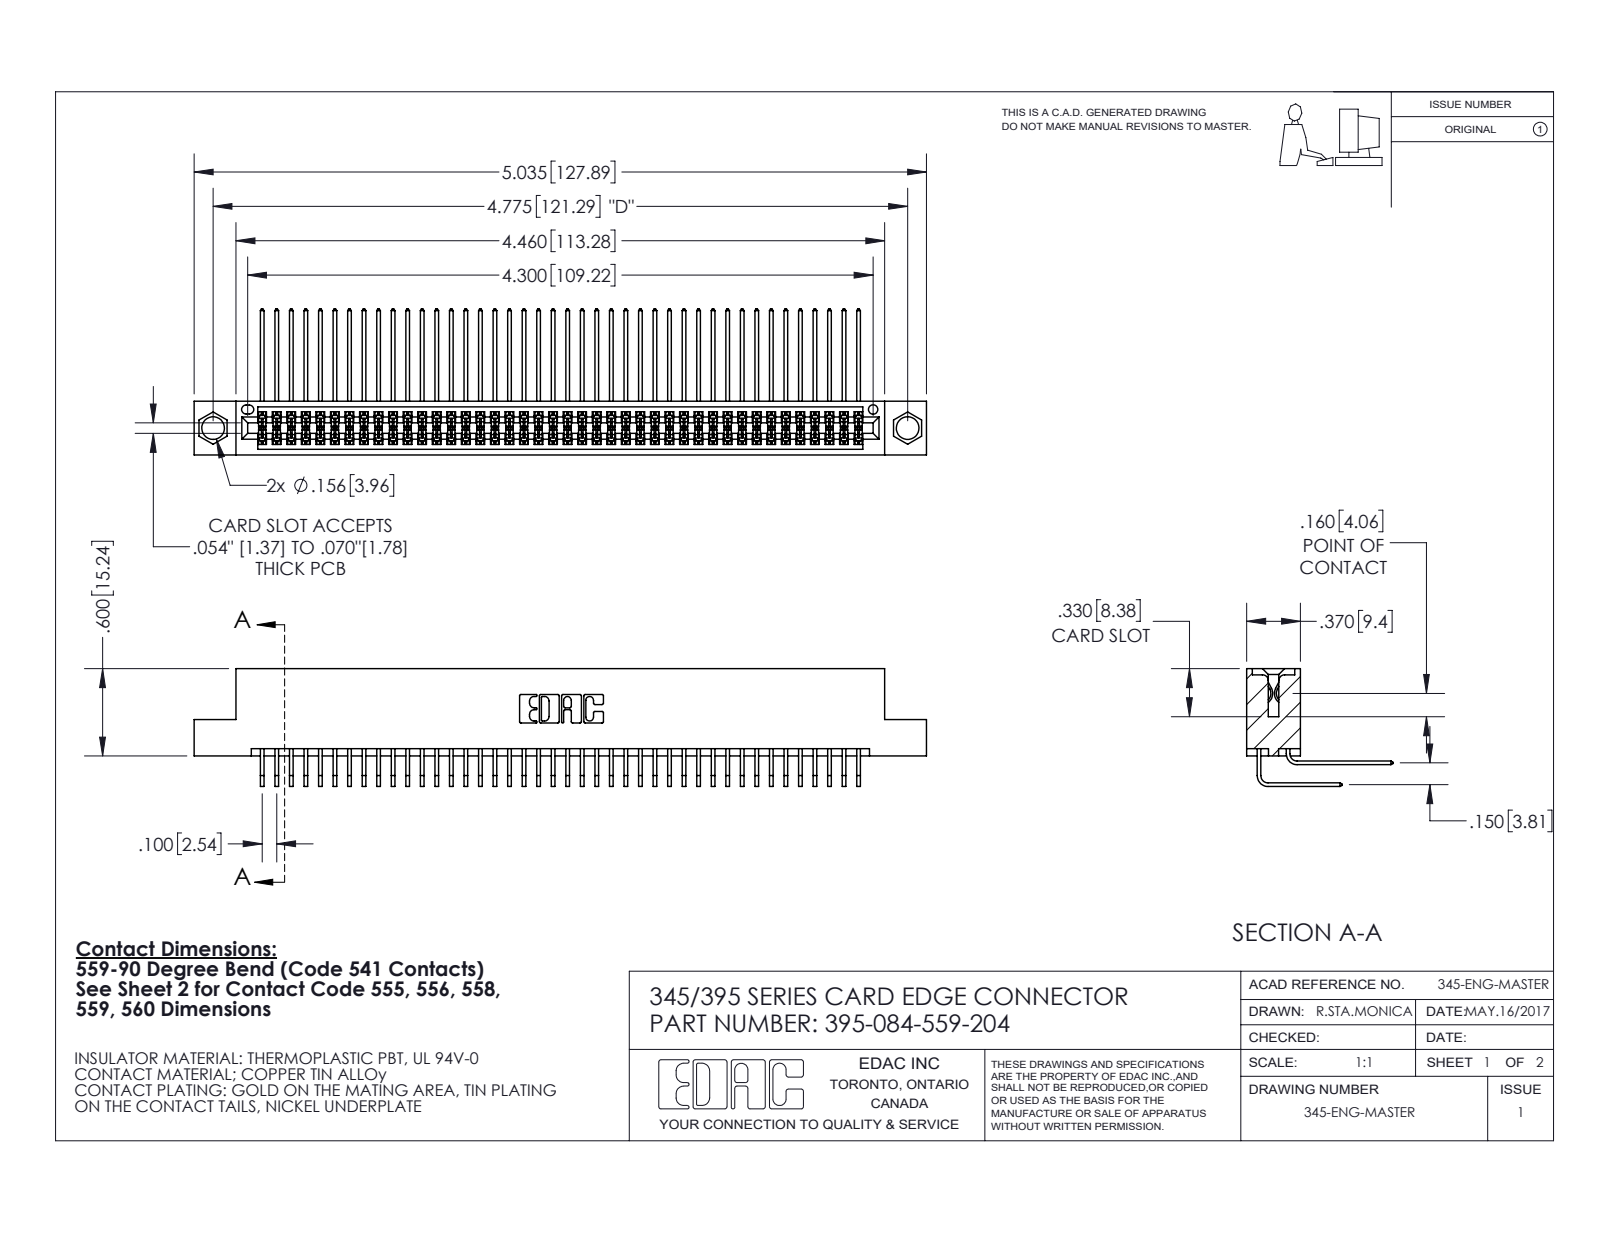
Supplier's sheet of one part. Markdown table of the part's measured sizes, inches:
| quantity | value |
| --- | --- |
| part name | 395-084-559-204; 345-292-001_559 Tail - 2; 345-292-001_558 559 Tail - 1; 345 Part_Flush Mounting Lugs - 0.156 Dia-TI |
| STEP written by | SolidWorks 2020 (CONFIG_CONTROL_DESIGN) |
| units | inches |
| bodies | 85 solids, 4508 faces (3034 planar, 1474 cylindrical, 0 other) |
| overall size | 5.035 × 1.005 × 0.809 |
| volume | 0.781 in³ |
| surface area | 32.63 in² |
| round holes (diameter × count) | 0.156 × 2, 0.064 × 1 |
| partial cylindrical surfaces (radius × count) | 0.006 × 168, 0.01 × 22, 0.007 × 6, 0.031 × 6, 0.026 × 3, 0.014 × 2, 0.019 × 2, 0.022 × 2 |
| main face-to-face distances | 0.072, 0.298, 0.2, 0.37, 0.098, 0.272, 0.025, 0.225, 0.175, 0.15 |
| hole center spacings | 0.27, 4.539, 4.775 |
